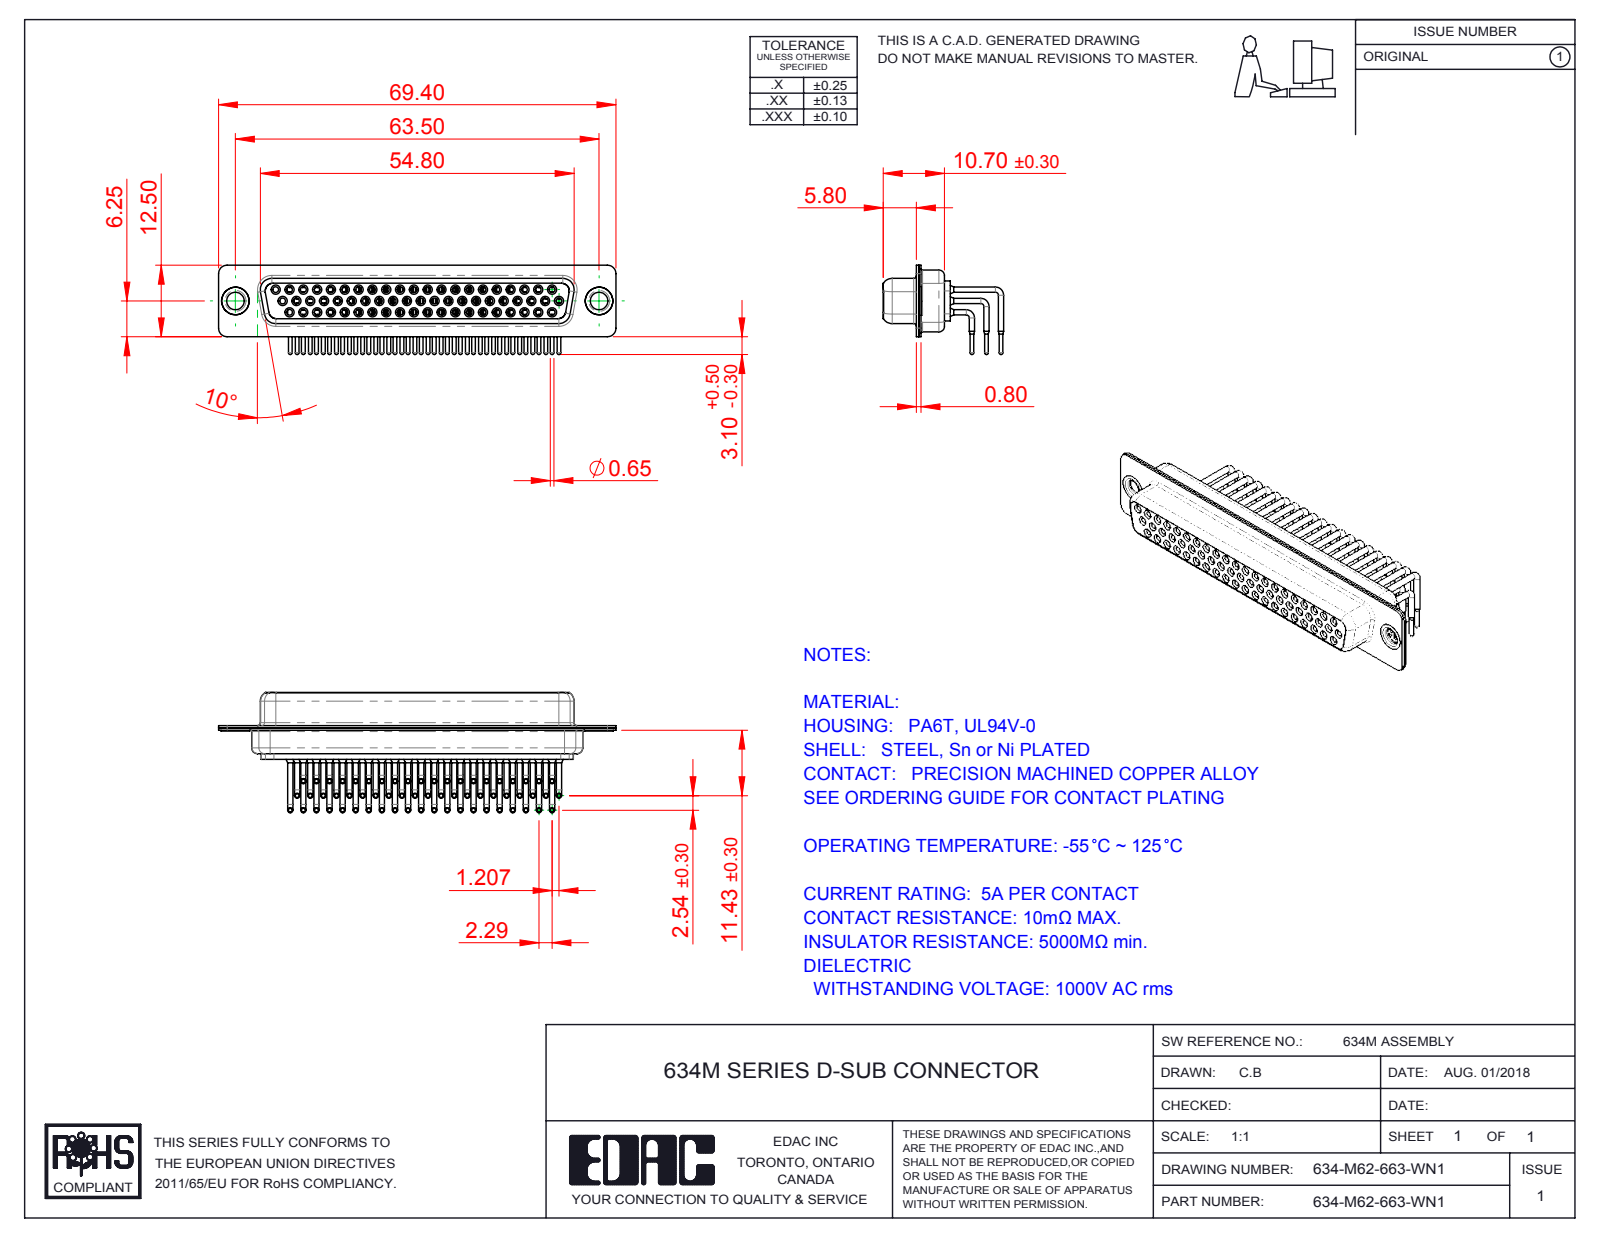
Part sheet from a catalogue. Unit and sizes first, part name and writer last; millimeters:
Units: millimetres
Overall size (bounding box): 69.4 × 21.02 × 15.6
Round holes (diameter × count): ⌀1 ×62, ⌀1.1 ×62, ⌀1.7 ×62, ⌀1.8 ×62, ⌀2 ×62, ⌀3.05 ×2, ⌀4 ×2, ⌀4.8 ×2
Round bosses / shafts (diameter × count): ⌀0.9 ×124, ⌀1.6 ×62, ⌀1.5 ×62, ⌀0.65 ×62, ⌀2 ×56, ⌀5 ×2, ⌀4.9 ×2, ⌀3.55 ×2
Partial cylindrical surfaces — rounded edges, fillets, slot ends (radius × count): R1.5 ×16, R2 ×12, R1.35 ×8, R1.6 ×8, R0.25 ×4, R0.5 ×4, R0.6 ×4, R0.65 ×4
Main face-to-face distances: 0.4, 1.45, 8.95, 1.9, 8.5, 2.3, 6.2, 0.45, 7.05, 0.85
Hole centre spacings: 7.24, 2.32, 2.41, 9.65, 4.13, 4.83, 16.89, 14.48
Volume: 5 326 mm³ · Surface area: 17 717 mm²
Bodies: 67 solids, 3539 faces (997 planar, 1547 cylindrical, 995 other)
Part name (STEP PRODUCT): 634M Shell Front_62 Contacts; 634M Housing_62 Contacts; 634M Contact Row 1; 634M Contact Row 3 (+4 more)
STEP written by: SolidWorks 2016 (CONFIG_CONTROL_DESIGN)
